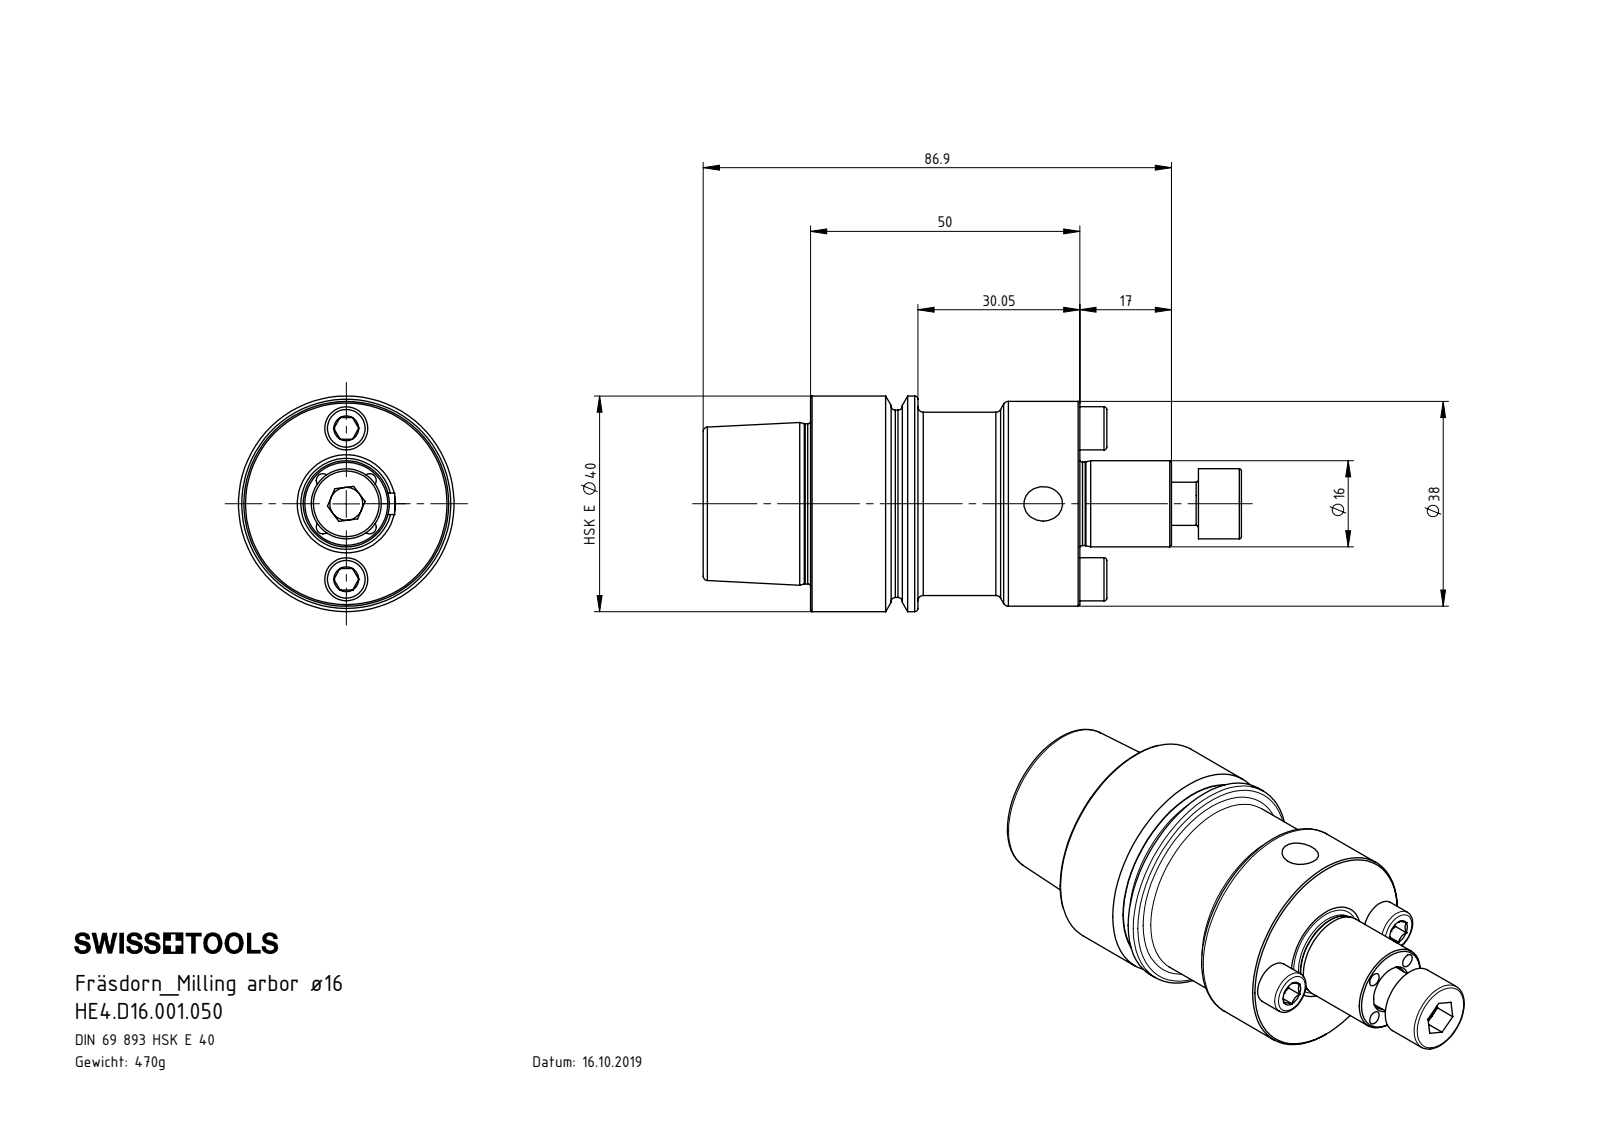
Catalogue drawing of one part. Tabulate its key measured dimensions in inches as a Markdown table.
| quantity | value |
| --- | --- |
| part name | D16-ER2.001.015_B; HE4-D16.001.050_A_Fertigbearbeitung; D16-ER1.002.025_A; HE4.D16.001.050 |
| STEP written by | SolidWorks 2017 (CONFIG_CONTROL_DESIGN) |
| units | inches |
| bodies | 4 solids, 239 faces (47 planar, 60 cylindrical, 132 other) |
| overall size | 3.933 × 1.575 × 1.575 |
| volume | 3.692 in³ |
| surface area | 26.8 in² |
| round holes (diameter × count) | 0.13 × 2, 0.236 × 2, 0.197 × 1, 0.268 × 1, 0.335 × 1, 0.433 × 1, 0.492 × 1, 0.827 × 1, 1.004 × 1 |
| round bosses / shafts (diameter × count) | 0.315 × 3, 0.157 × 2, 0.118 × 2, 1.575 × 1, 1.496 × 1, 1.368 × 1, 1.339 × 1, 1.17 × 1 |
| main face-to-face distances | 1.969, 0.472, 0.313, 1.656, 0.783, 1.096, 2.752, 1.569, 0.785, 1.183 |
| hole center spacings | 0.551, 1.102 |
